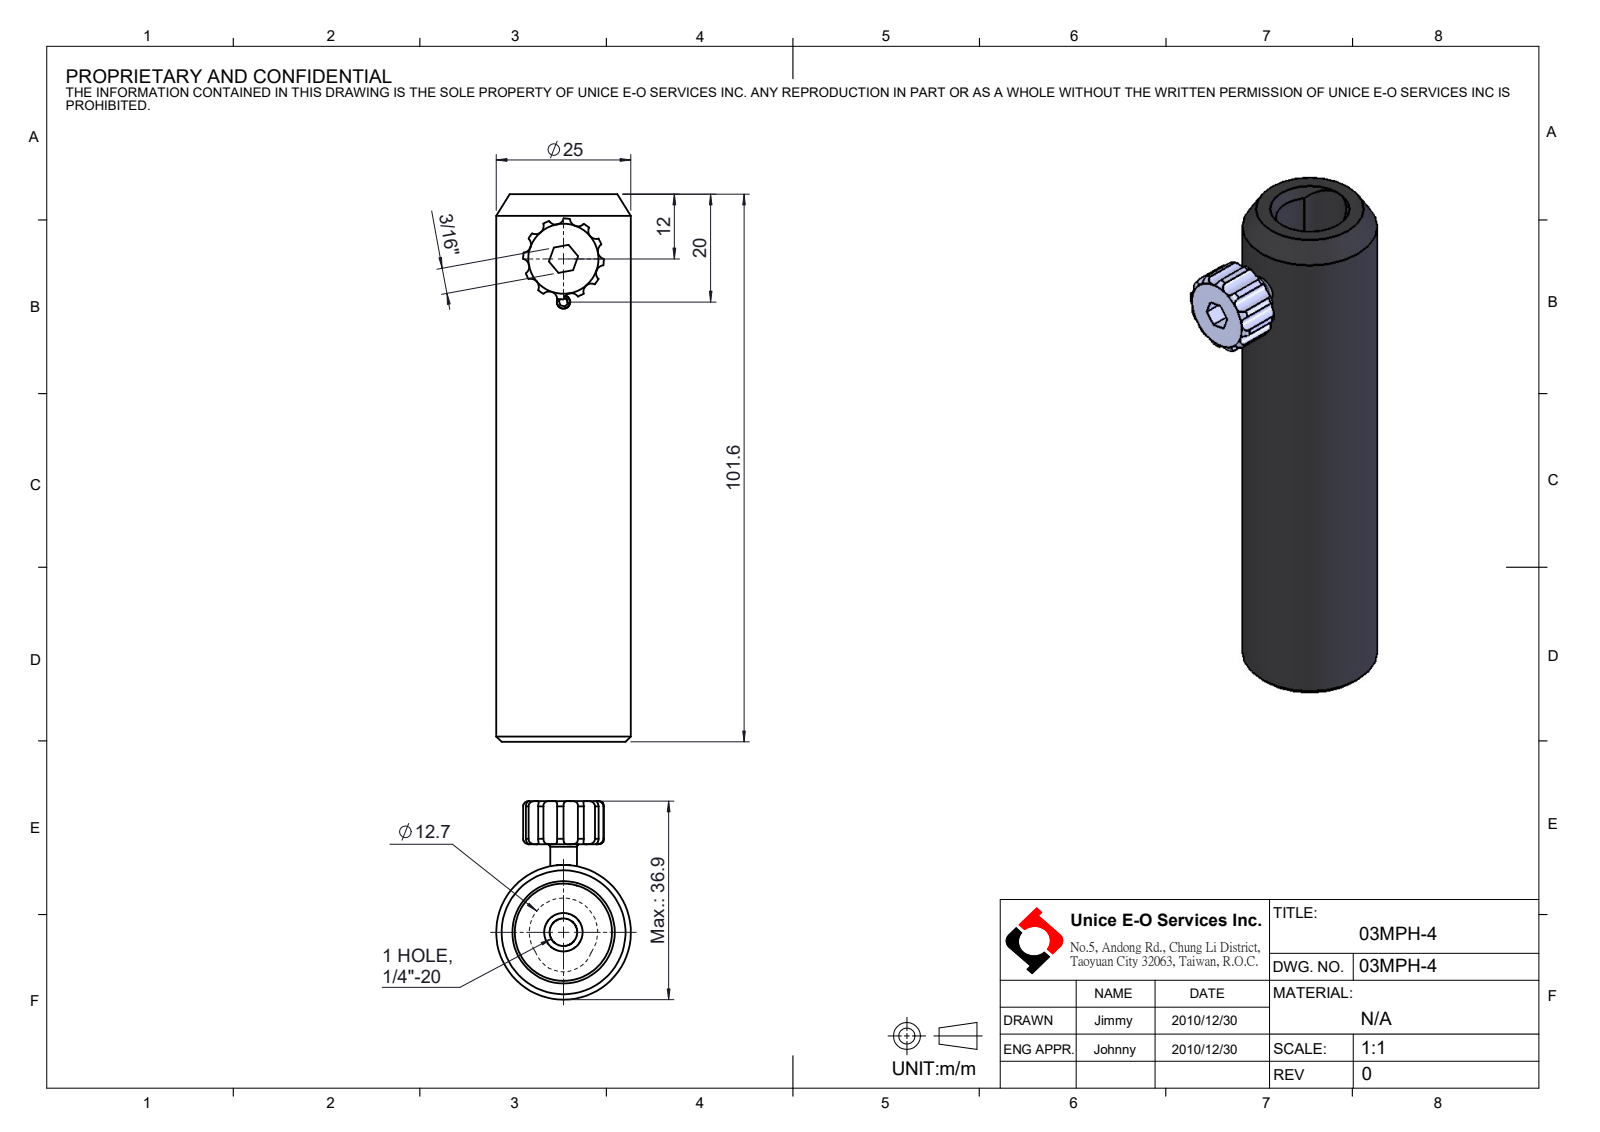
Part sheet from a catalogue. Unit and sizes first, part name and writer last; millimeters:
Units: millimetres
Overall size (bounding box): 101.6 × 36.85 × 25
Round holes (diameter × count): ⌀5.11 ×1, ⌀19 ×1
Round bosses / shafts (diameter × count): ⌀25 ×1, ⌀4.94 ×1
Partial cylindrical surfaces — rounded edges, fillets, slot ends (radius × count): R1.5 ×12, R5.5 ×1, R6.35 ×1, R7.5 ×1
Main face-to-face distances: 101.6, 8, 4.76, 3.85, 11.85, 1.5
Bodies: 0 solids, 94 faces (16 planar, 40 cylindrical, 38 other)
Part name (STEP PRODUCT): 03MPH-4
STEP written by: SolidWorks 2016 (CONFIG_CONTROL_DESIGN)
